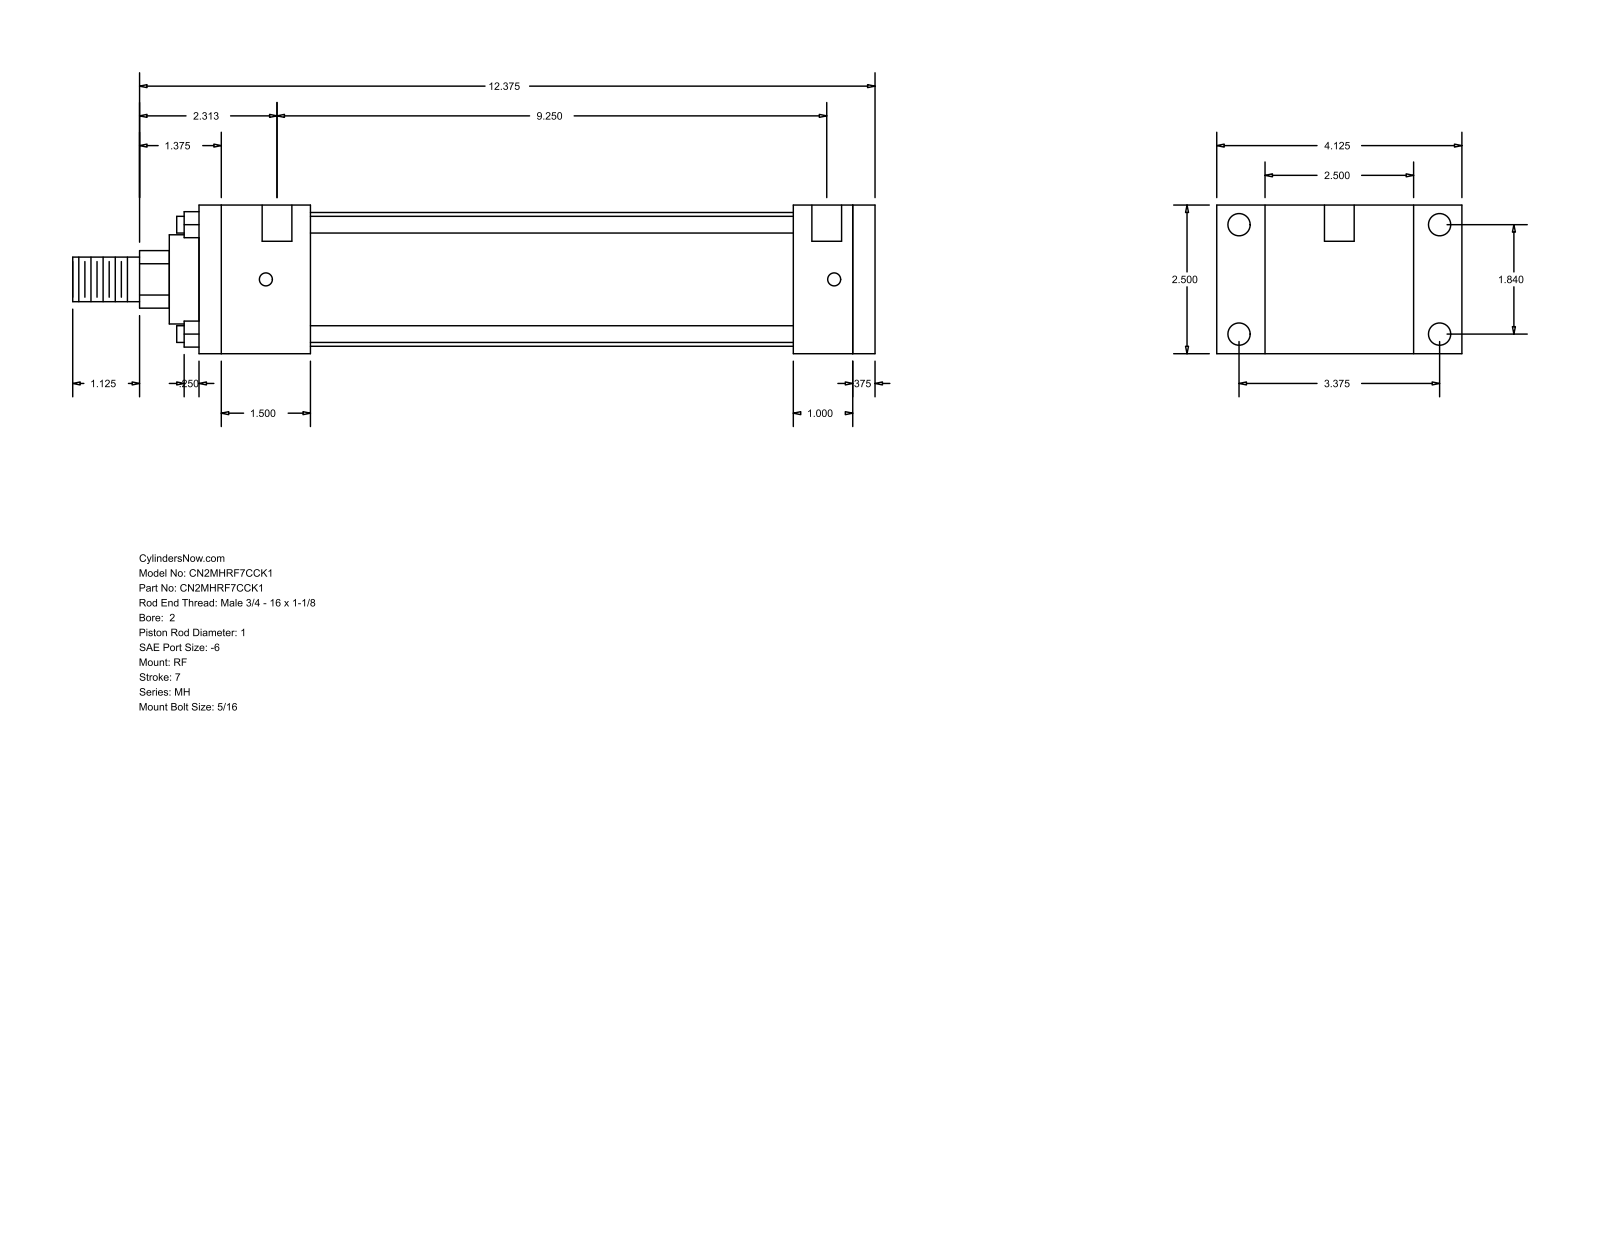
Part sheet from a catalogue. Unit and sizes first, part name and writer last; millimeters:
Units: millimetres
Overall size (bounding box): 342.9 × 104.78 × 63.5
Round holes (diameter × count): ⌀5.56 ×4, ⌀9.53 ×4, ⌀12.7 ×2
Round bosses / shafts (diameter × count): ⌀7.14 ×4, ⌀57.15 ×1, ⌀38.1 ×1, ⌀25.4 ×1, ⌀19.05 ×1
Partial cylindrical surfaces — rounded edges, fillets, slot ends (radius × count): R12.29 ×1
Main face-to-face distances: 63.5, 288.92, 9.52, 279.4, 20.64, 25.4, 47.63, 254, 206.37, 231.77
Hole centre spacings: 46.74, 85.72, 97.63, 242.88, 3.17, 4.76, 234.95, 238.12
Bodies: 0 solids, 92 faces (64 planar, 28 cylindrical, 0 other)
Part name (STEP PRODUCT): MH_RF__0200_1
STEP written by: GSSL Pune (CONFIG_CONTROL_DESIGN)
